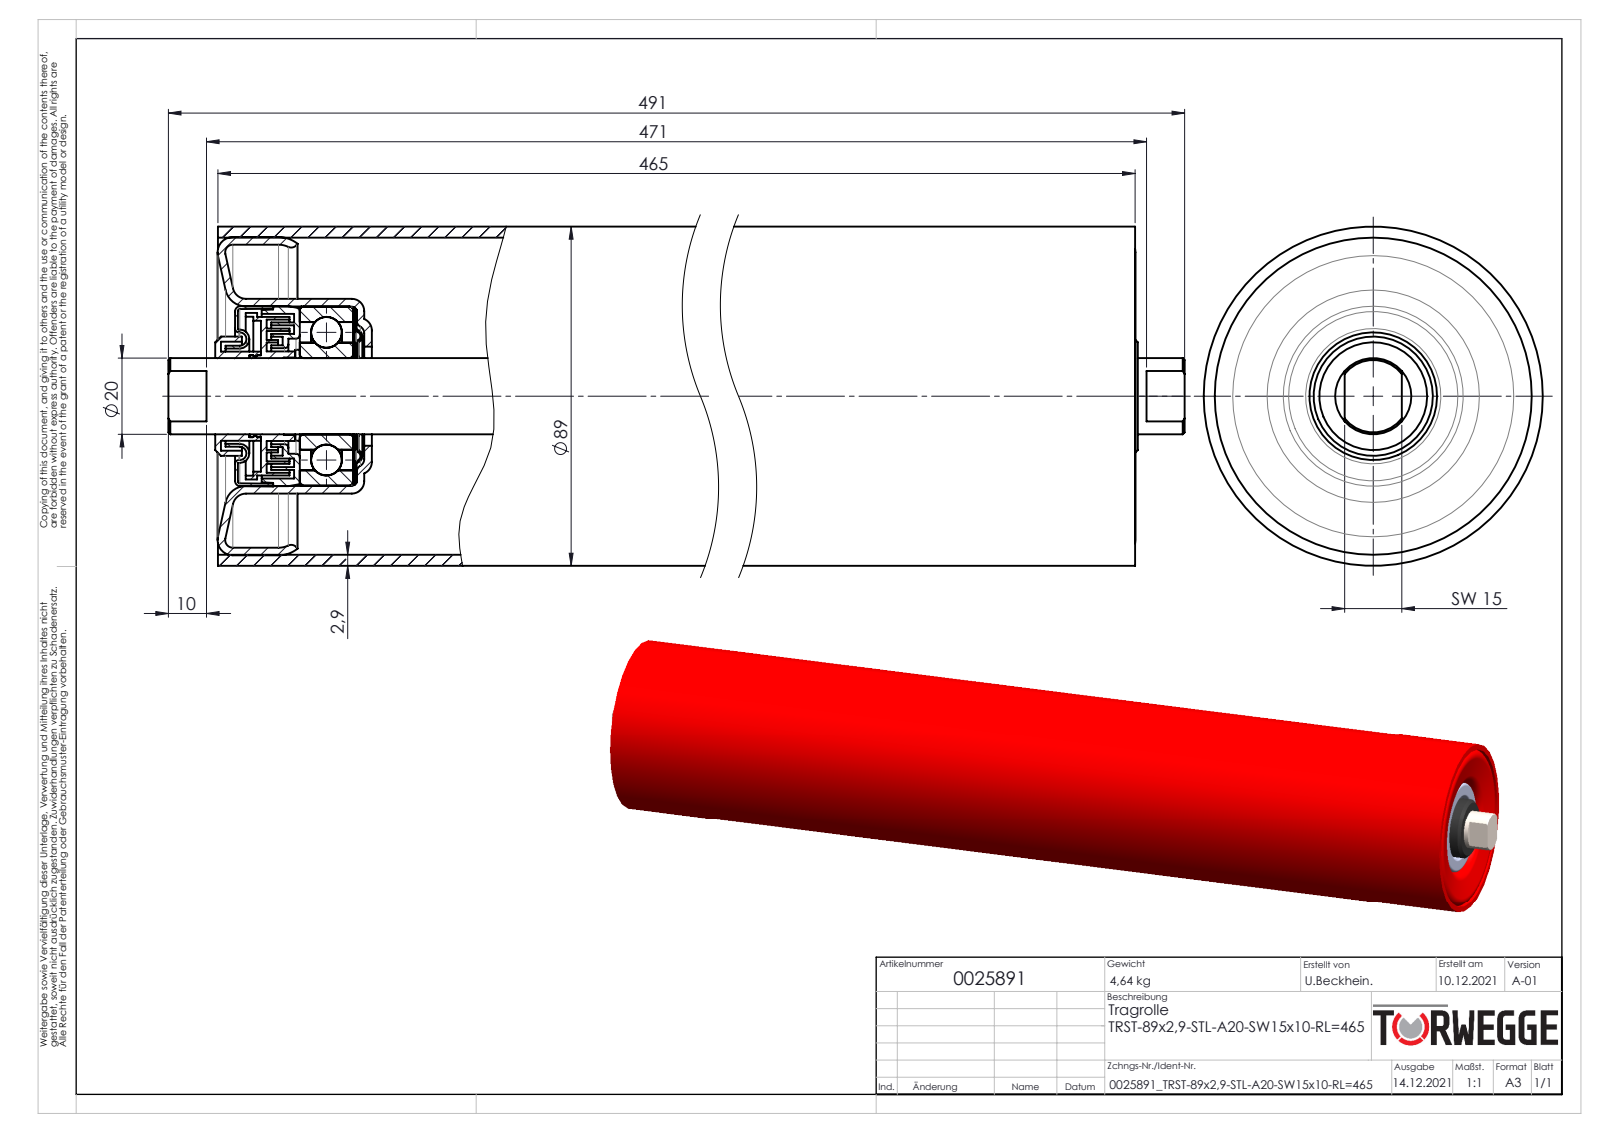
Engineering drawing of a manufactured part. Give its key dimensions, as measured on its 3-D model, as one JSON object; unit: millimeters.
{"part_name": "0025891", "step_written_by": "SolidWorks 2020 (AUTOMOTIVE_DESIGN)", "units": "millimeters", "bodies": {"solids": 24, "faces": 606, "planar": 114, "cylindrical": 244, "other": 248}, "overall_size": [491, 89, 89], "volume_mm3": 670846, "surface_area_mm2": 439349, "round_holes": [[2, 4], [19, 1], [19.6, 1], [20, 1], [20.3, 1], [21, 1], [21.5, 1], [25, 1], [25.2, 1], [26, 1], [28.2, 1], [28.6, 1]], "round_bosses_or_shafts": [[23.9, 2], [89, 1], [83.5, 1], [51.1, 1], [47.2, 1], [47, 1], [46.5, 1], [43.7, 1]], "partial_cylinders_radius": [[2, 8], [13.5, 1]], "face_to_face_distances": [14, 408.02, 14.92, 407.1, 0.92, 393.1, 422.02, 10.2, 24.2, 25.12], "hole_center_spacings": [11.49, 11.5, 22.55, 3.99, 4, 21.43, 22.99]}
